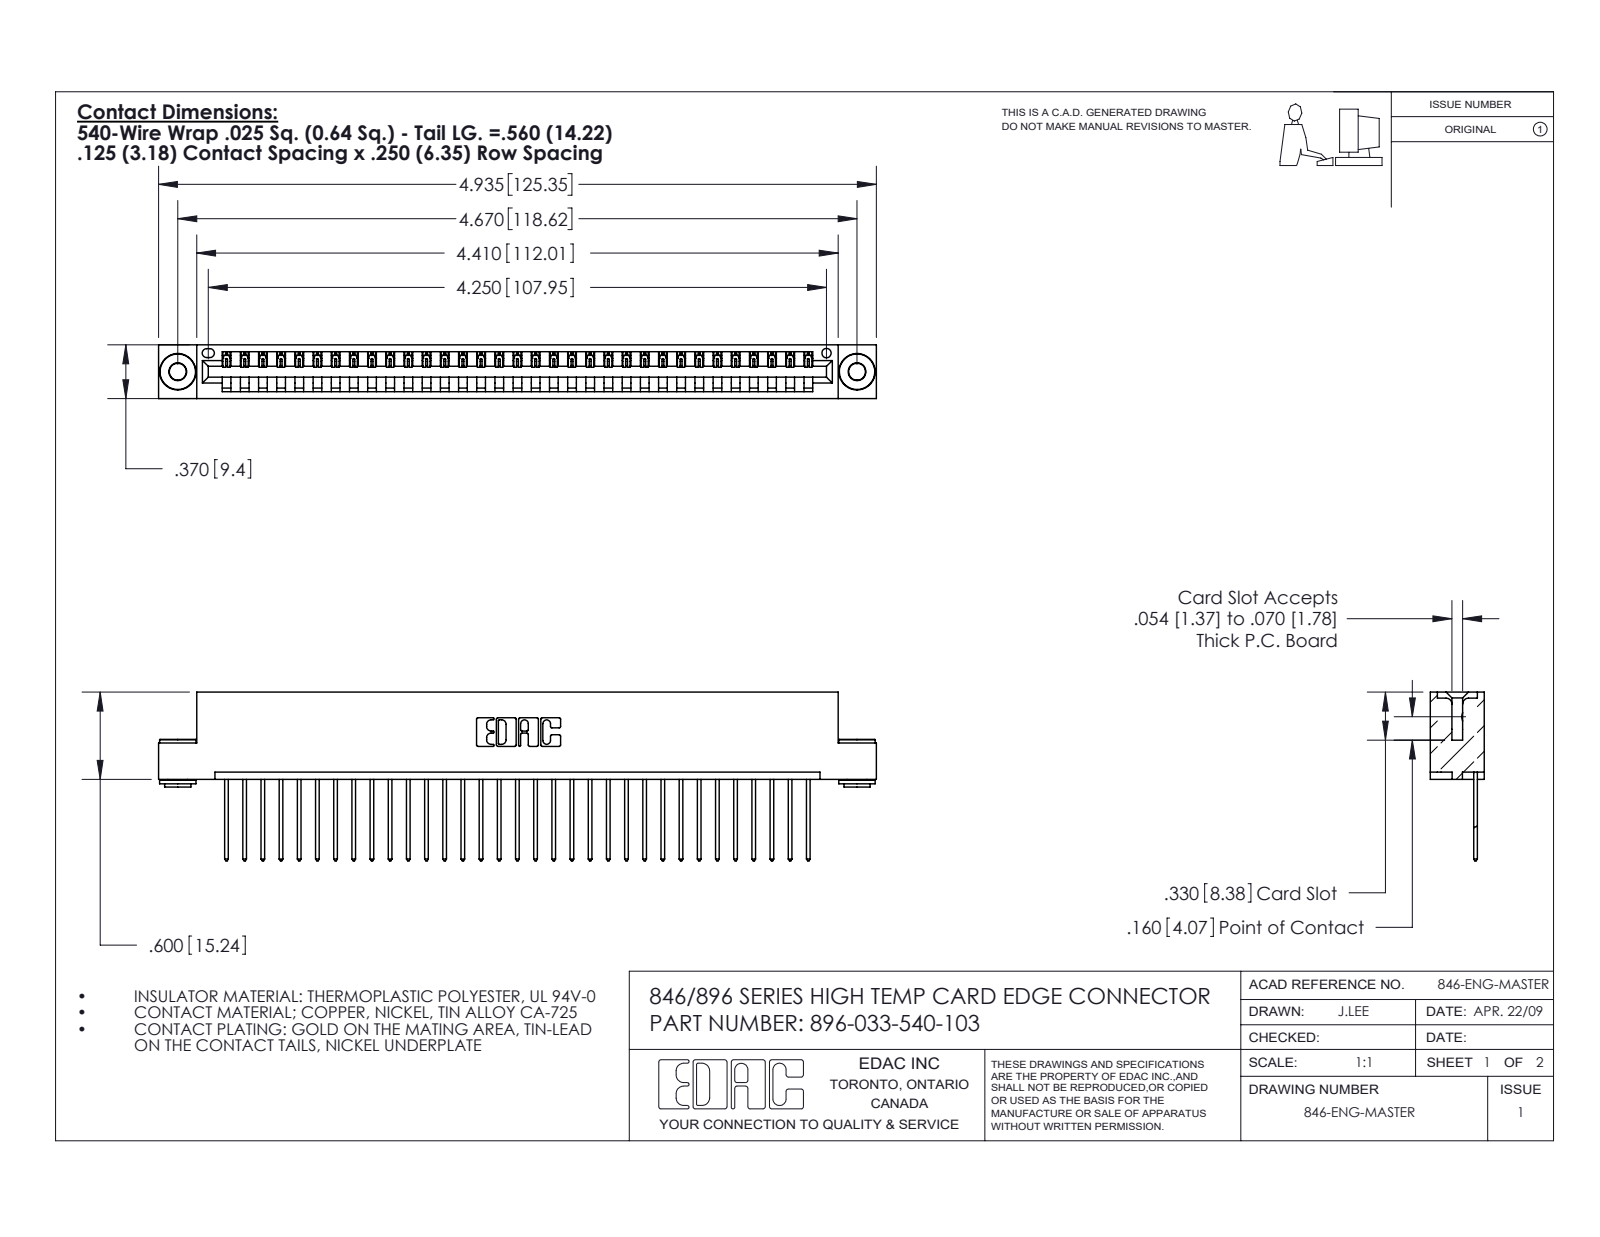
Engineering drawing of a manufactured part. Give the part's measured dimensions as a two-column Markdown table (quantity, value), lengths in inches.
| quantity | value |
| --- | --- |
| part name | 345-250-002_345-250-002-102; 345-292-001_345-293-140; 396-033-540-103; 346 Part_Flush Mounting Lugs - 0.156 Dia-TH |
| STEP written by | SolidWorks 2016 (CONFIG_CONTROL_DESIGN) |
| units | inches |
| bodies | 36 solids, 2074 faces (1406 planar, 660 cylindrical, 8 other) |
| overall size | 4.935 × 1.16 × 0.37 |
| volume | 0.732 in³ |
| surface area | 23.94 in² |
| round holes (diameter × count) | 0.116 × 2, 0.156 × 2, 0.064 × 1 |
| round bosses / shafts (diameter × count) | 0.25 × 2, 0.18 × 2, 0.136 × 2 |
| partial cylindrical surfaces (radius × count) | 0.006 × 66, 0.01 × 66, 0.01 × 22, 0.007 × 6, 0.031 × 6, 0.026 × 3, 0.031 × 2, 0.04 × 2 |
| main face-to-face distances | 0.048, 0.322, 0.37, 0.25, 0.025, 0.072, 0.298, 0.148, 0.222, 0.1 |
| hole center spacings | 0.246, 4.462, 4.67 |
